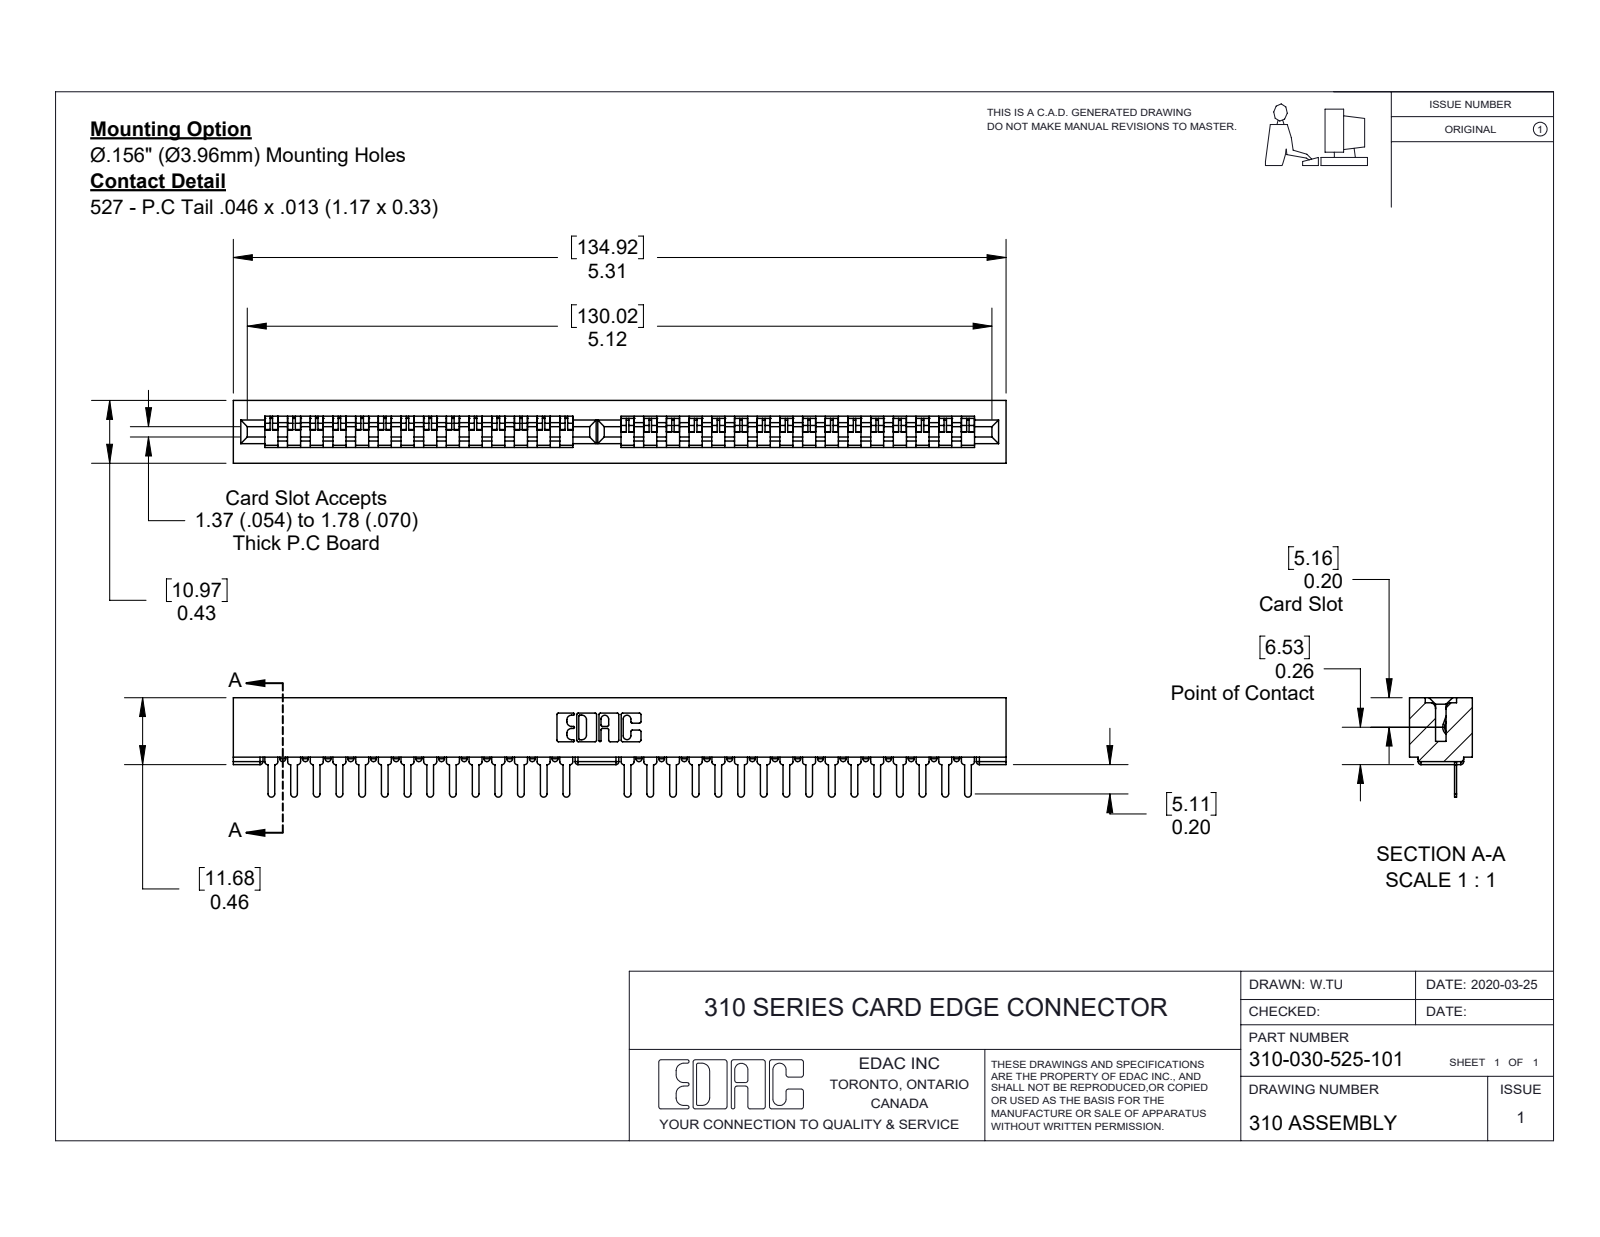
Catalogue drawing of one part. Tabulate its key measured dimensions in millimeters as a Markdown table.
| quantity | value |
| --- | --- |
| part name | 310 Part_No Mounting Lugs; 310-030-525-101; 307-290-001_525 |
| STEP written by | SolidWorks 2016 (CONFIG_CONTROL_DESIGN) |
| units | millimeters |
| bodies | 31 solids, 1838 faces (1190 planar, 584 cylindrical, 64 other) |
| overall size | 134.93 × 17.37 × 10.97 |
| volume | 11 645 mm³ |
| surface area | 13 868 mm² |
| partial cylindrical surfaces (radius × count) | 0.51 × 158, 0.58 × 30, 0.25 × 22, 0.17 × 6, 0.8 × 6, 0.67 × 3, 0.3 × 2, 0.64 × 2 |
| main face-to-face distances | 2.76, 8.22, 10.98, 0.38, 1.82, 0.33, 10.38, 5.46, 4.58, 6.4 |
